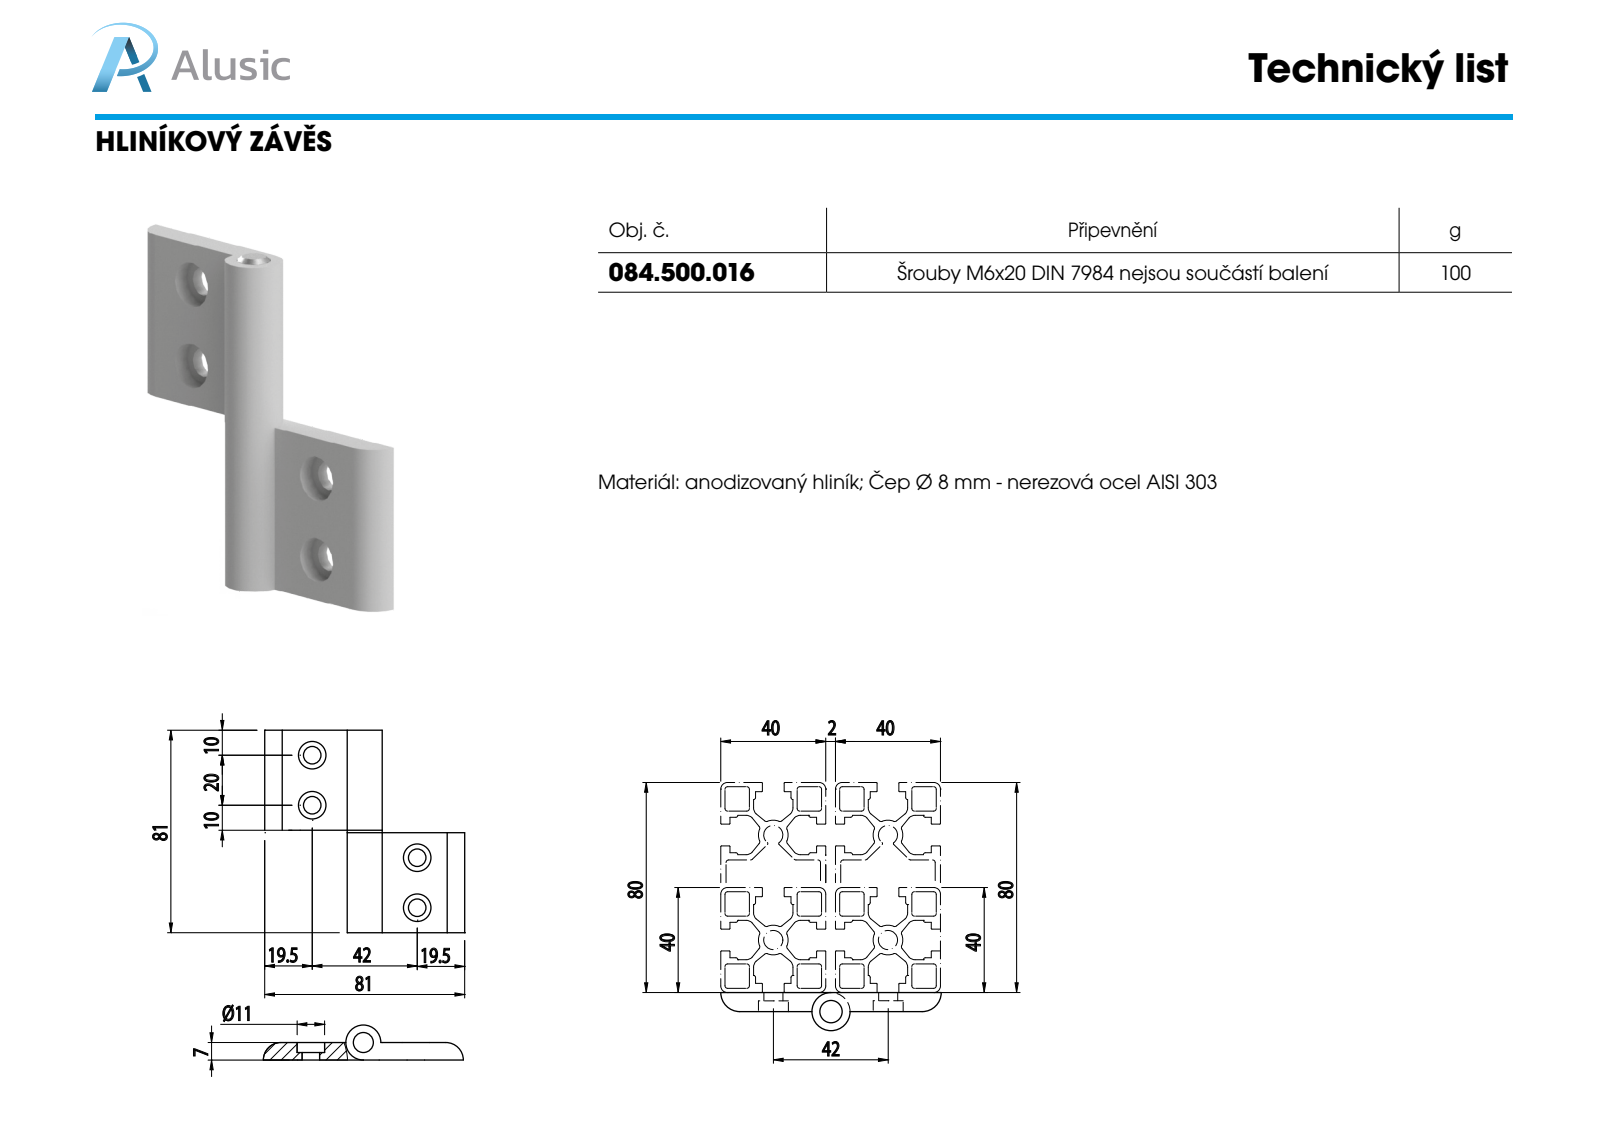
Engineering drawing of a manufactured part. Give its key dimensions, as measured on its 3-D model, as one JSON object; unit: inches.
{"part_name": "084.500.016; PERNO CERNIERA_084.500.001.B; SEMI CERNIERA_084.500.016A", "step_written_by": "SolidWorks 2012 (CONFIG_CONTROL_DESIGN)", "units": "inches", "bodies": {"solids": 3, "faces": 166, "planar": 134, "cylindrical": 28, "other": 4}, "overall_size": [3.189, 3.189, 0.551], "volume_in3": 1.764, "surface_area_in2": 23.15, "round_holes": [[0.276, 4], [0.433, 4], [0.323, 1]], "round_bosses_or_shafts": [[0.551, 1], [0.315, 1]], "partial_cylinders_radius": [[0.276, 2]], "face_to_face_distances": [0.276, 1.575, 3.15, 0.118, 0.157, 0.241, 3.189, 1.614, 0.039, 0.241], "hole_center_spacings": [0.787, 2.283, 1.831, 2.883]}
